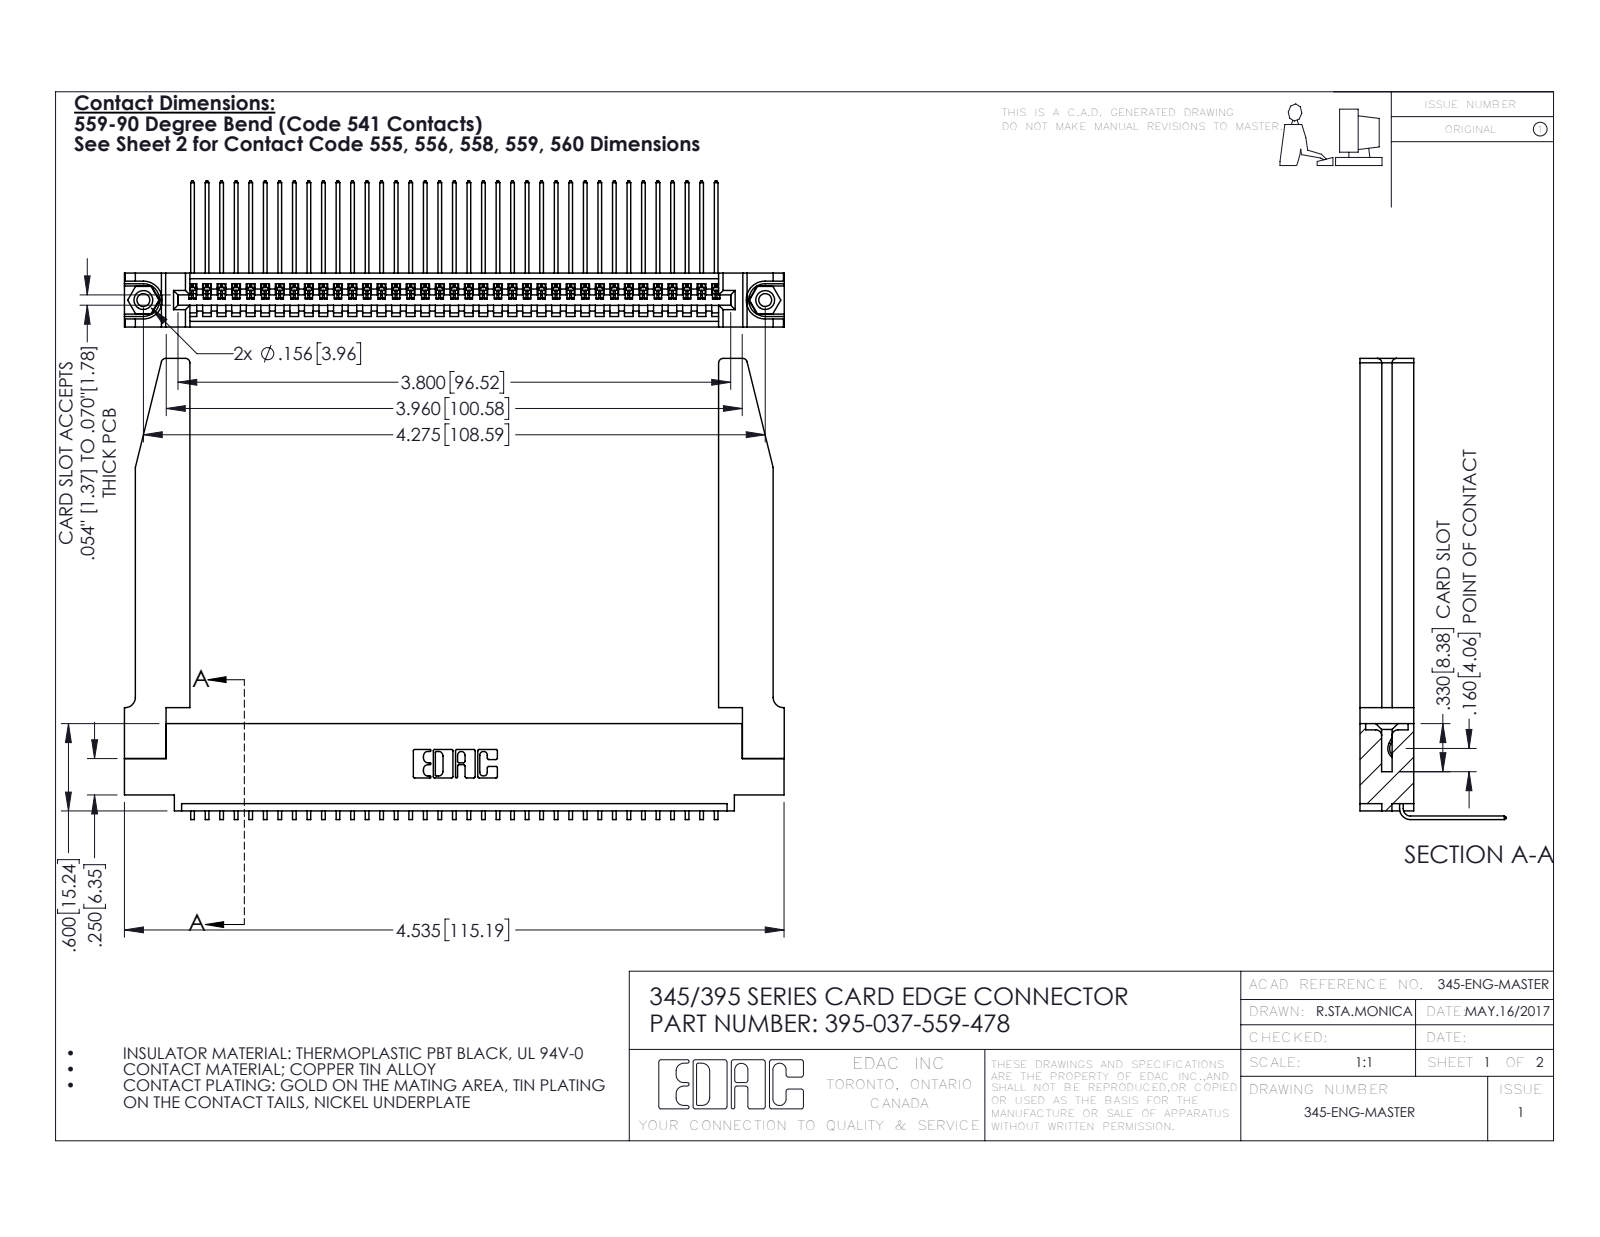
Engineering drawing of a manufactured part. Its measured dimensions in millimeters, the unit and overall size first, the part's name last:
Units: millimetres
Overall size (bounding box): 115.2 × 80.5 × 25.5
Round holes (diameter × count): ⌀2.3 ×2, ⌀3.2 ×2, ⌀4 ×2, ⌀1.6 ×1
Round bosses / shafts (diameter × count): ⌀3.9 ×2
Partial cylindrical surfaces — rounded edges, fillets, slot ends (radius × count): R0.2 ×74, R0.3 ×22, R0.8 ×8, R0.2 ×6, R0.8 ×6, R0.7 ×3, R0.8 ×2, R1 ×2
Main face-to-face distances: 9.4, 1.8, 7.6, 2.5, 6.9, 0.6, 5.1, 5.7, 3.8, 3.8
Hole centre spacings: 6.9, 102.6, 108.6
Volume: 18 730 mm³ · Surface area: 22 140 mm²
Bodies: 42 solids, 2584 faces (1780 planar, 752 cylindrical, 52 other)
Part name (STEP PRODUCT): 345 Part_0.110 Offset - 0.156 Dia-TH; 345-292-001_558 559 Tail - 1; 345-220-078_345-220-078; 345-250-001_345-250-001-102 (+1 more)
STEP written by: SolidWorks 2016 (CONFIG_CONTROL_DESIGN)
